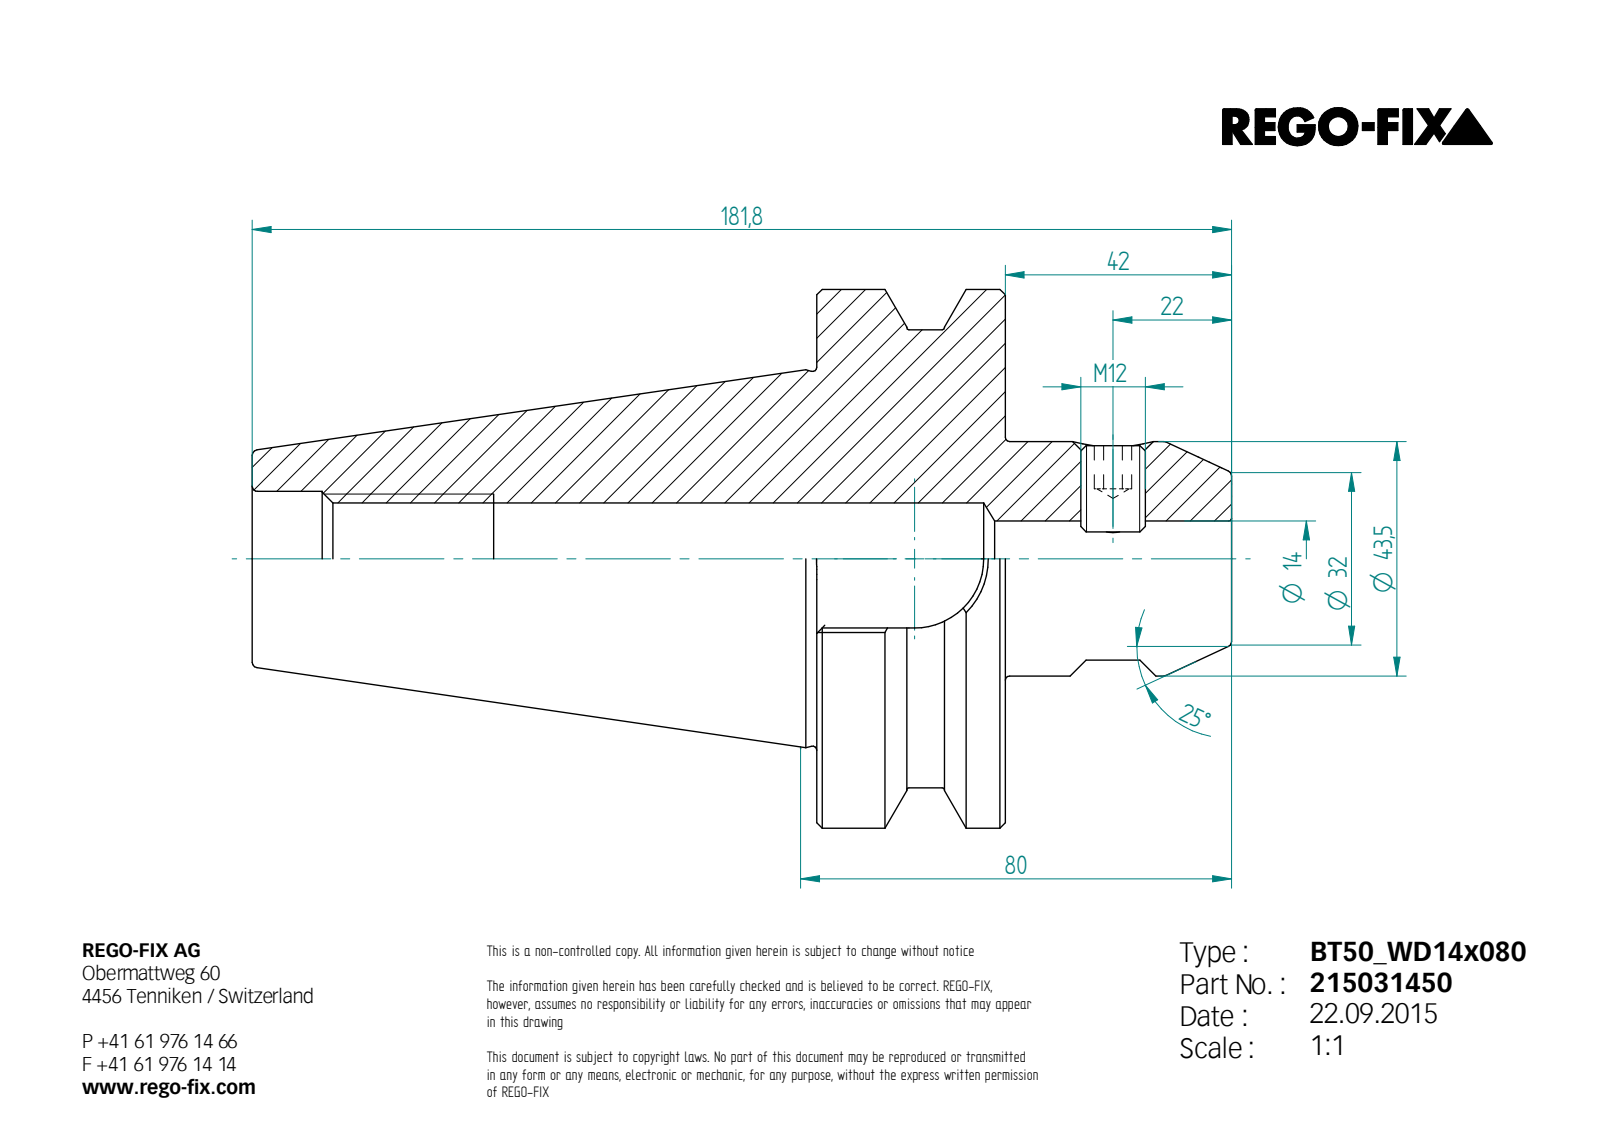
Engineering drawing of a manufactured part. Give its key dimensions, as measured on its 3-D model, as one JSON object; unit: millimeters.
{"step_written_by": "Unknown (AUTOMOTIVE_DESIGN)", "units": "millimeters", "bodies": {"solids": 2, "faces": 94, "planar": 45, "cylindrical": 18, "other": 31}, "overall_size": [181.8, 100, 100], "volume_mm3": 495972, "surface_area_mm2": 61390, "round_holes": [[10.11, 1], [14, 1], [20.75, 1], [25, 1]], "round_bosses_or_shafts": [[100, 1], [85, 1], [43.5, 1], [12, 1]], "partial_cylinders_radius": [[0.5, 4], [12.85, 1]], "face_to_face_distances": [35, 70.7, 104.8, 139.8, 181.8, 77, 42, 25.7, 5.95, 31.65]}
